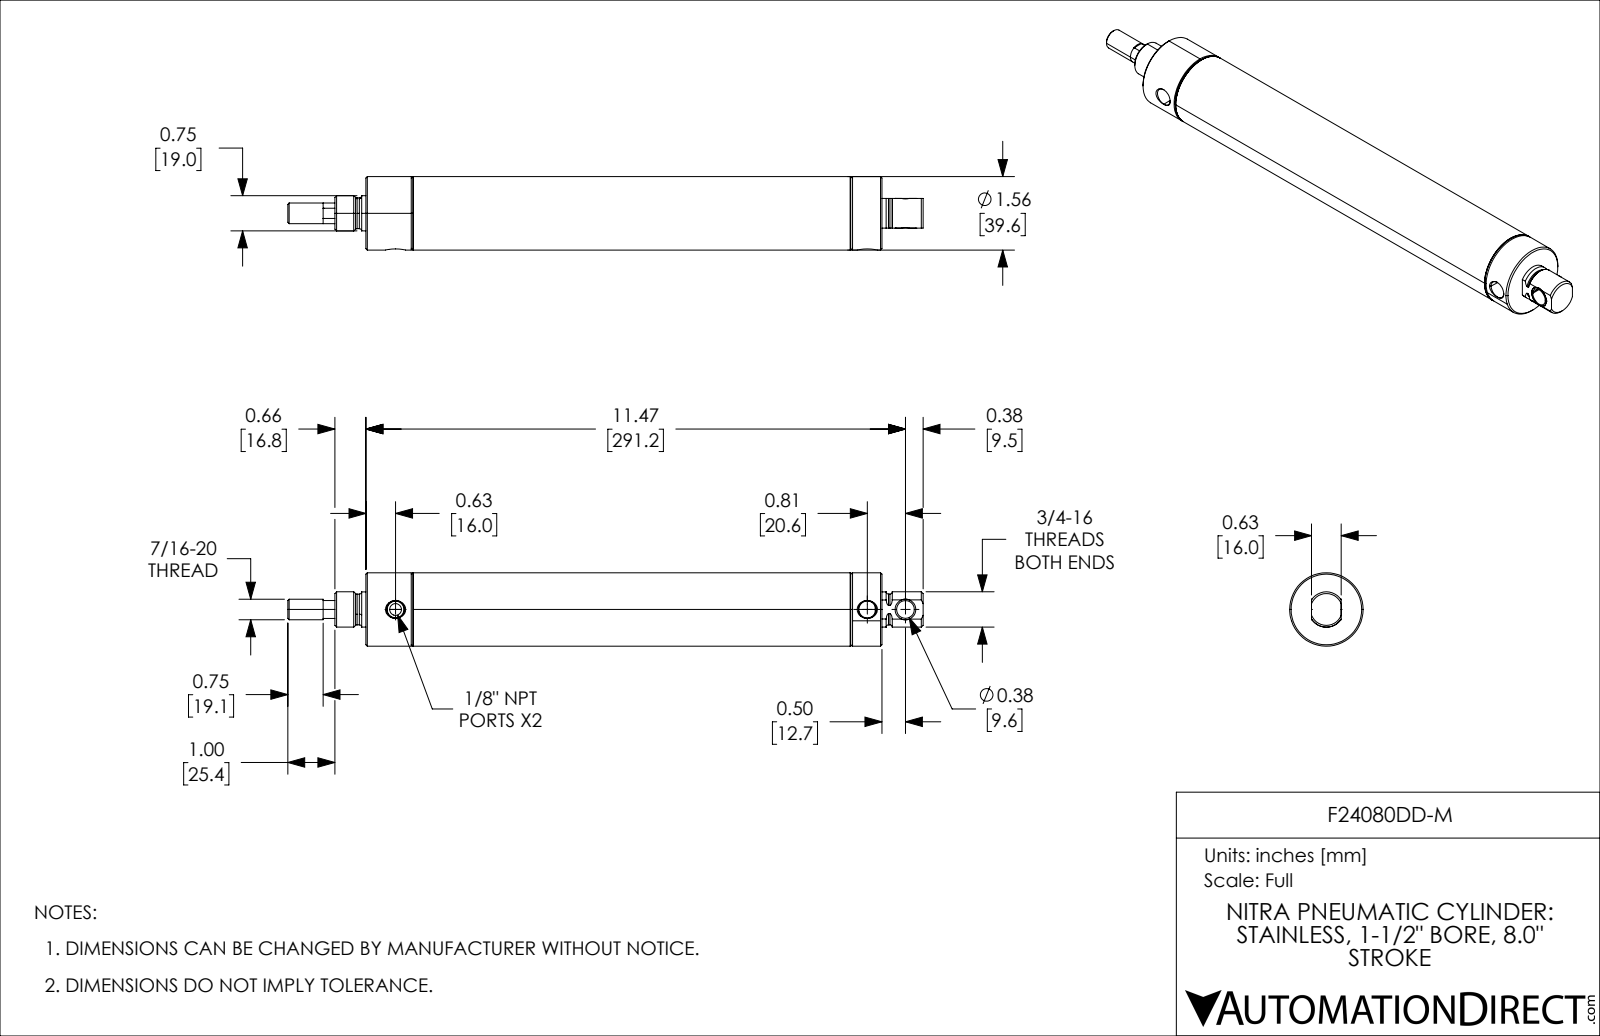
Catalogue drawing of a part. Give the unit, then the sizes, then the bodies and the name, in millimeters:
Units: millimetres
Overall size (bounding box): 342.9 × 39.62 × 39.62
Round holes (diameter × count): ⌀6.35 ×1, ⌀9.14 ×1, ⌀9.55 ×1, ⌀11.15 ×1, ⌀11.73 ×1, ⌀13.51 ×1, ⌀26.97 ×1, ⌀36.36 ×1
Round bosses / shafts (diameter × count): ⌀39.62 ×1, ⌀38.39 ×1, ⌀19.05 ×1, ⌀18.99 ×1, ⌀16.61 ×1, ⌀16.6 ×1, ⌀11.13 ×1, ⌀11.11 ×1
Main face-to-face distances: 22.22, 44.45, 203.2, 225.42, 247.65, 22.23, 30.86, 234.06, 256.28, 278.51
Hole centre spacings: 20.57, 254.64, 275.21
Volume: 130 704 mm³ · Surface area: 92 517 mm²
Bodies: 5 solids, 157 faces (35 planar, 58 cylindrical, 64 other)
Part name (STEP PRODUCT): F24080DD-M; F24080DD-M_3; F24080DD-M_5; F24080DD-M_11 (+2 more)
STEP written by: SolidWorks 2021 (CONFIG_CONTROL_DESIGN)
